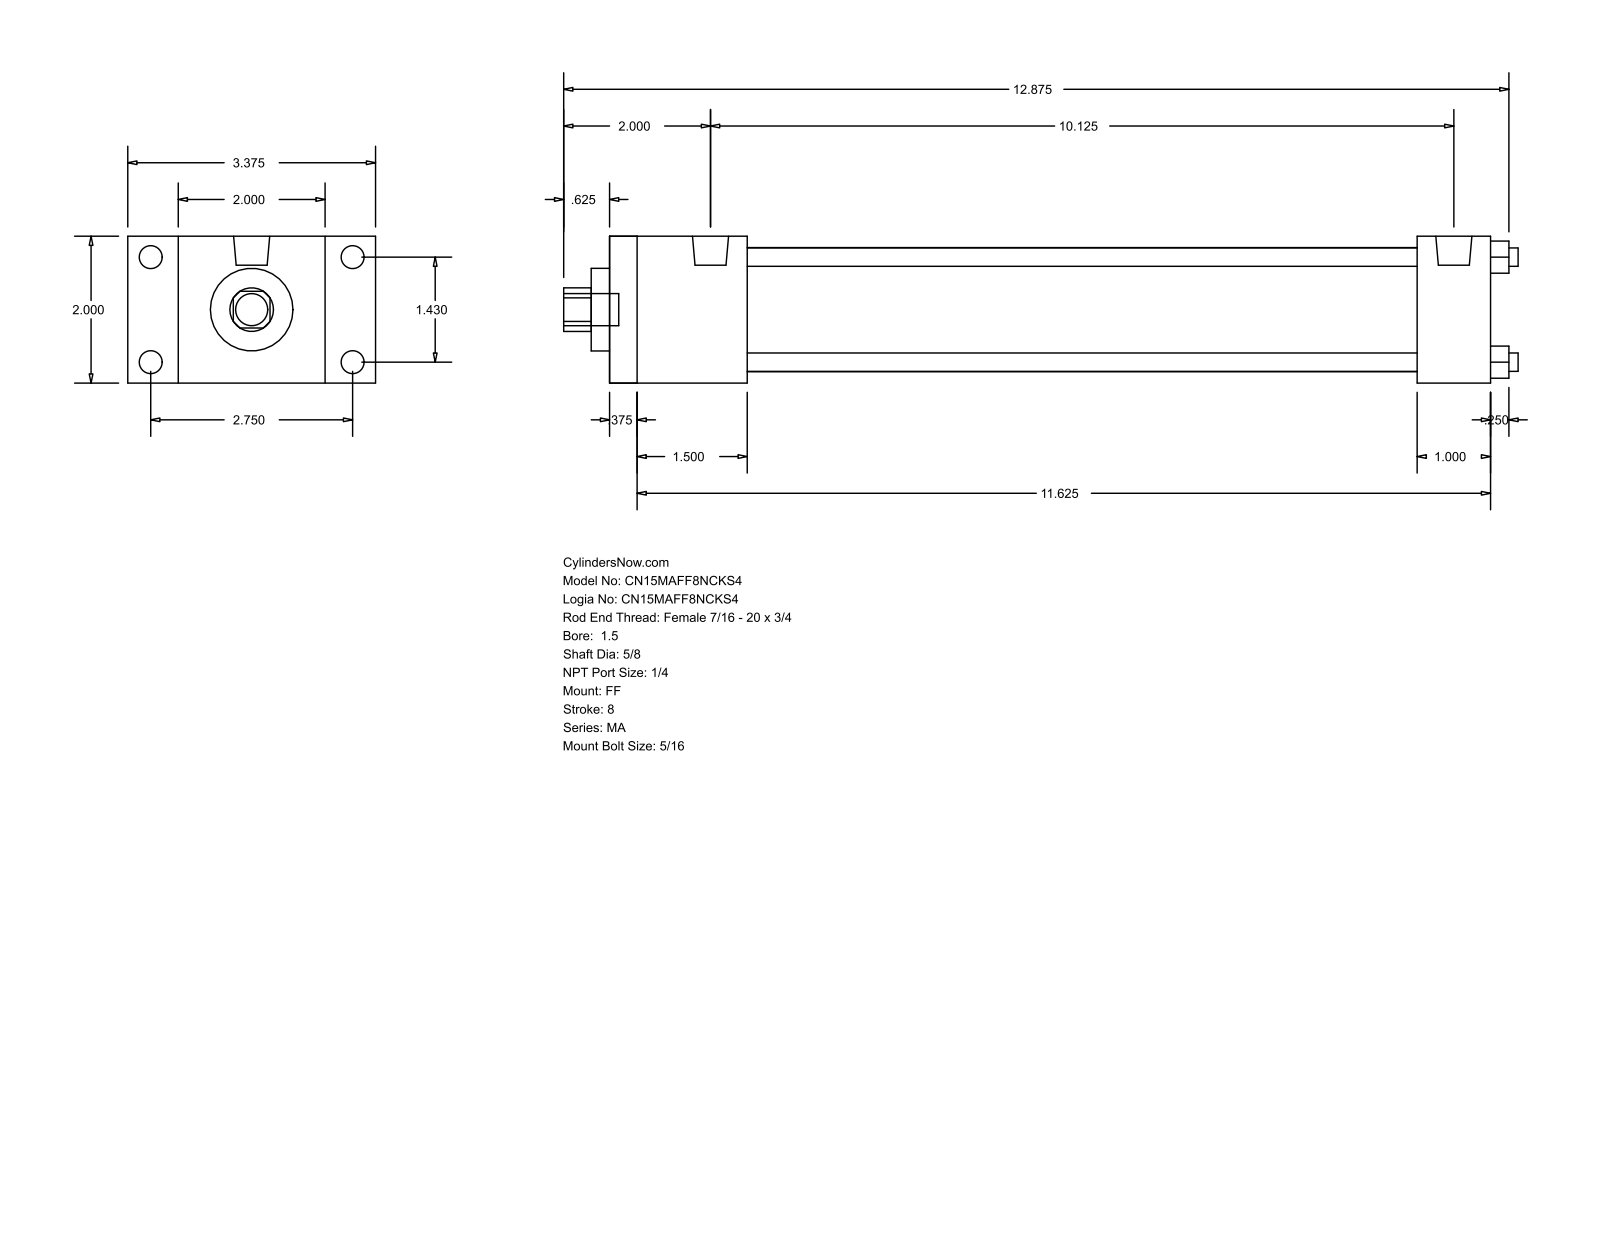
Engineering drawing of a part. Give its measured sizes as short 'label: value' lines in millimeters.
name: MA_FF__0150_0.625
written by: GSSL Pune (CONFIG_CONTROL_DESIGN)
unit: mm
bodies: 0 solids, 92 faces (64 planar, 28 cylindrical, 0 other)
size: 330.2 × 85.72 × 50.8
holes: 4× ⌀6.35, 1× ⌀15.88, 1× ⌀28.57, 1× ⌀42.93
bosses: 8× ⌀7.94, 2× ⌀12.49, 1× ⌀11.11
rounds: 1× R7.54
face distances: 50.8, 304.8, 9.52, 295.28, 47.62, 279.39, 38.1, 269.87, 231.77, 257.18
hole spacings: 25.68, 36.32, 51.36
